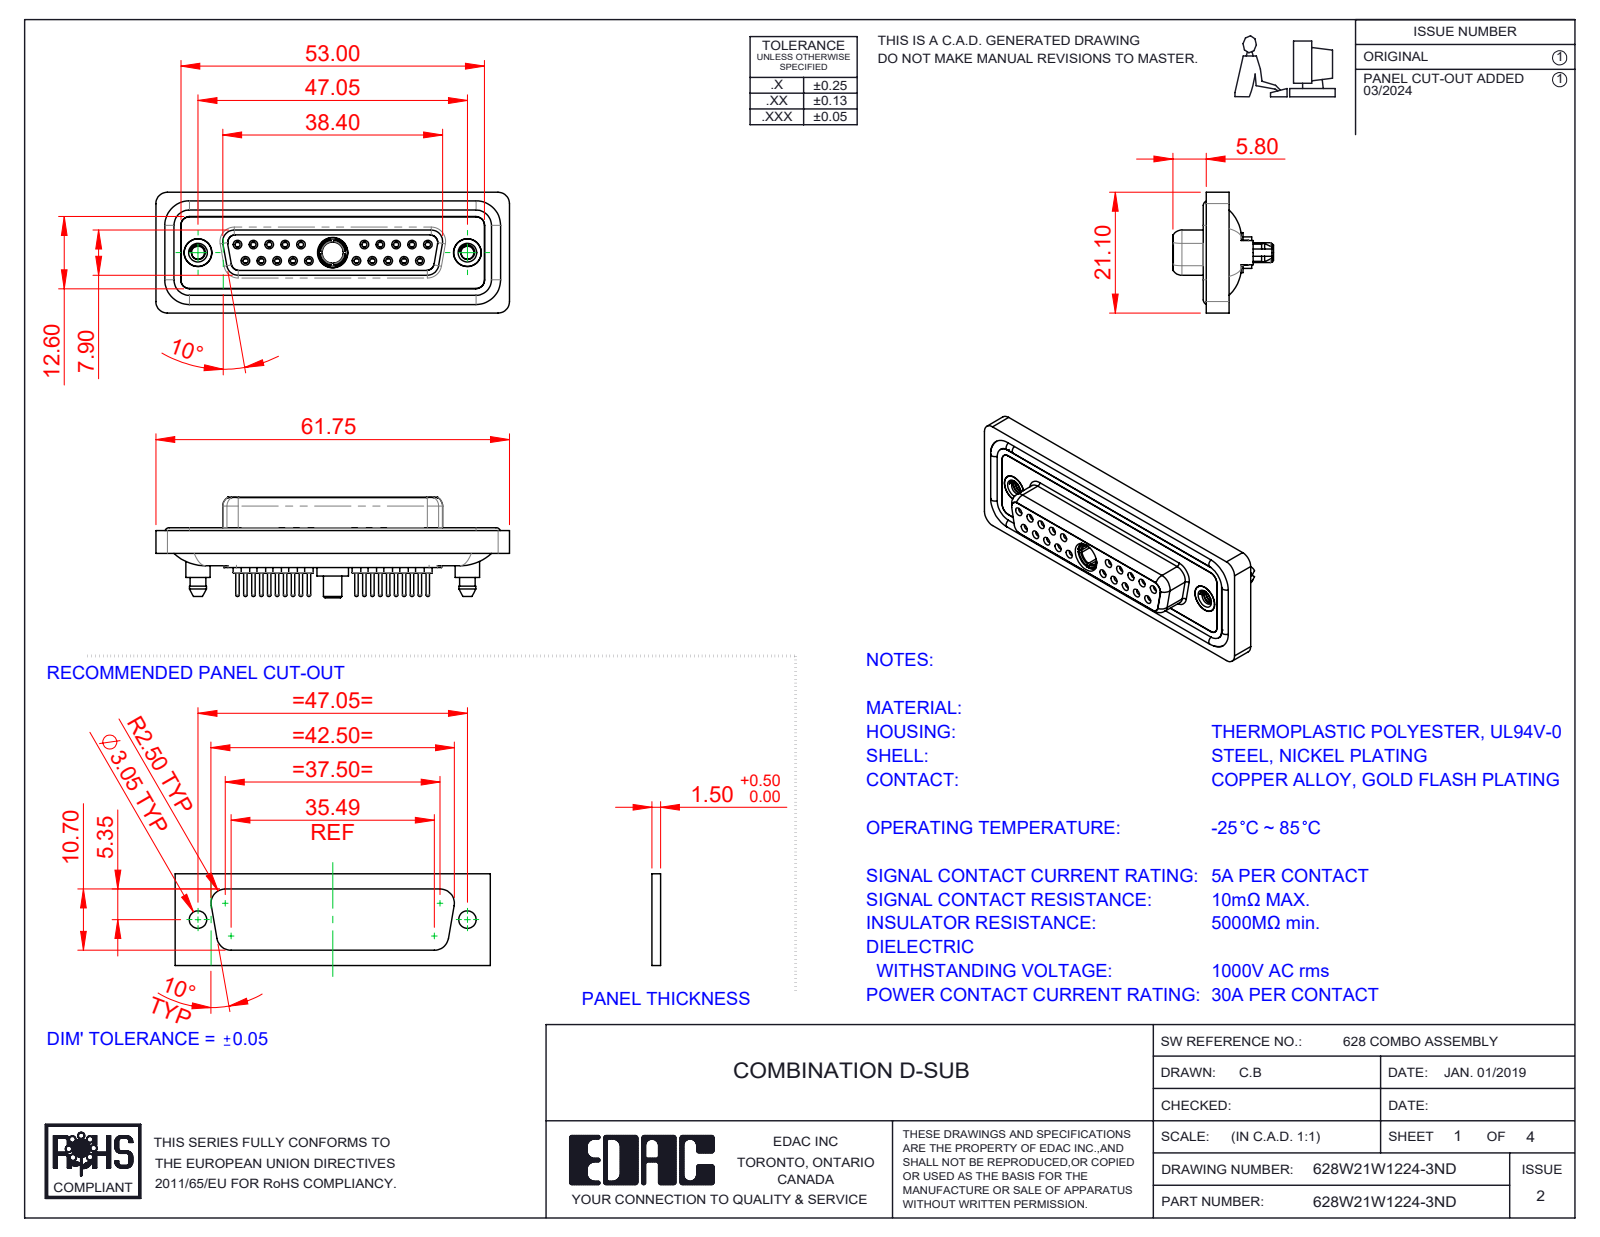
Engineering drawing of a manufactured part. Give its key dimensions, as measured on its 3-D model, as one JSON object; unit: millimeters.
{"part_name": "628Combo Shell Rear_25 Contacts; 628Combo Contact Row 1_24; 628Combo Contact Row 2_24; 628Combo Shell Front_25 Contacts (+5 more)", "step_written_by": "SolidWorks 2023 (CONFIG_CONTROL_DESIGN)", "units": "millimeters", "bodies": {"solids": 29, "faces": 1626, "planar": 450, "cylindrical": 639, "other": 537}, "overall_size": [61.75, 21.1, 17.55], "volume_mm3": 8517, "surface_area_mm2": 14346, "round_holes": [[0.9, 20], [1.1, 20], [1.5, 20], [2, 20], [1.6, 10], [1.7, 10], [4.85, 3], [2.26, 2], [4, 2], [4.05, 2], [5, 2], [3.7, 1]], "round_bosses_or_shafts": [[2.2, 20], [0.6, 20], [1.6, 14], [5.4, 2], [4.95, 2], [4.8, 2], [4.25, 2], [5.5, 1]], "partial_cylinders_radius": [[1.5, 24], [2, 18], [1.6, 10], [1.35, 8], [0.25, 4], [0.5, 4], [0.6, 4], [0.65, 4]], "face_to_face_distances": [0.4, 1.8, 7.45, 6.6, 5.65, 1.6, 0.5, 7.05, 2.9, 1.1], "hole_center_spacings": [3.16, 2.77, 5.54, 5.03, 8.31, 7.48, 16.62, 19.39]}
